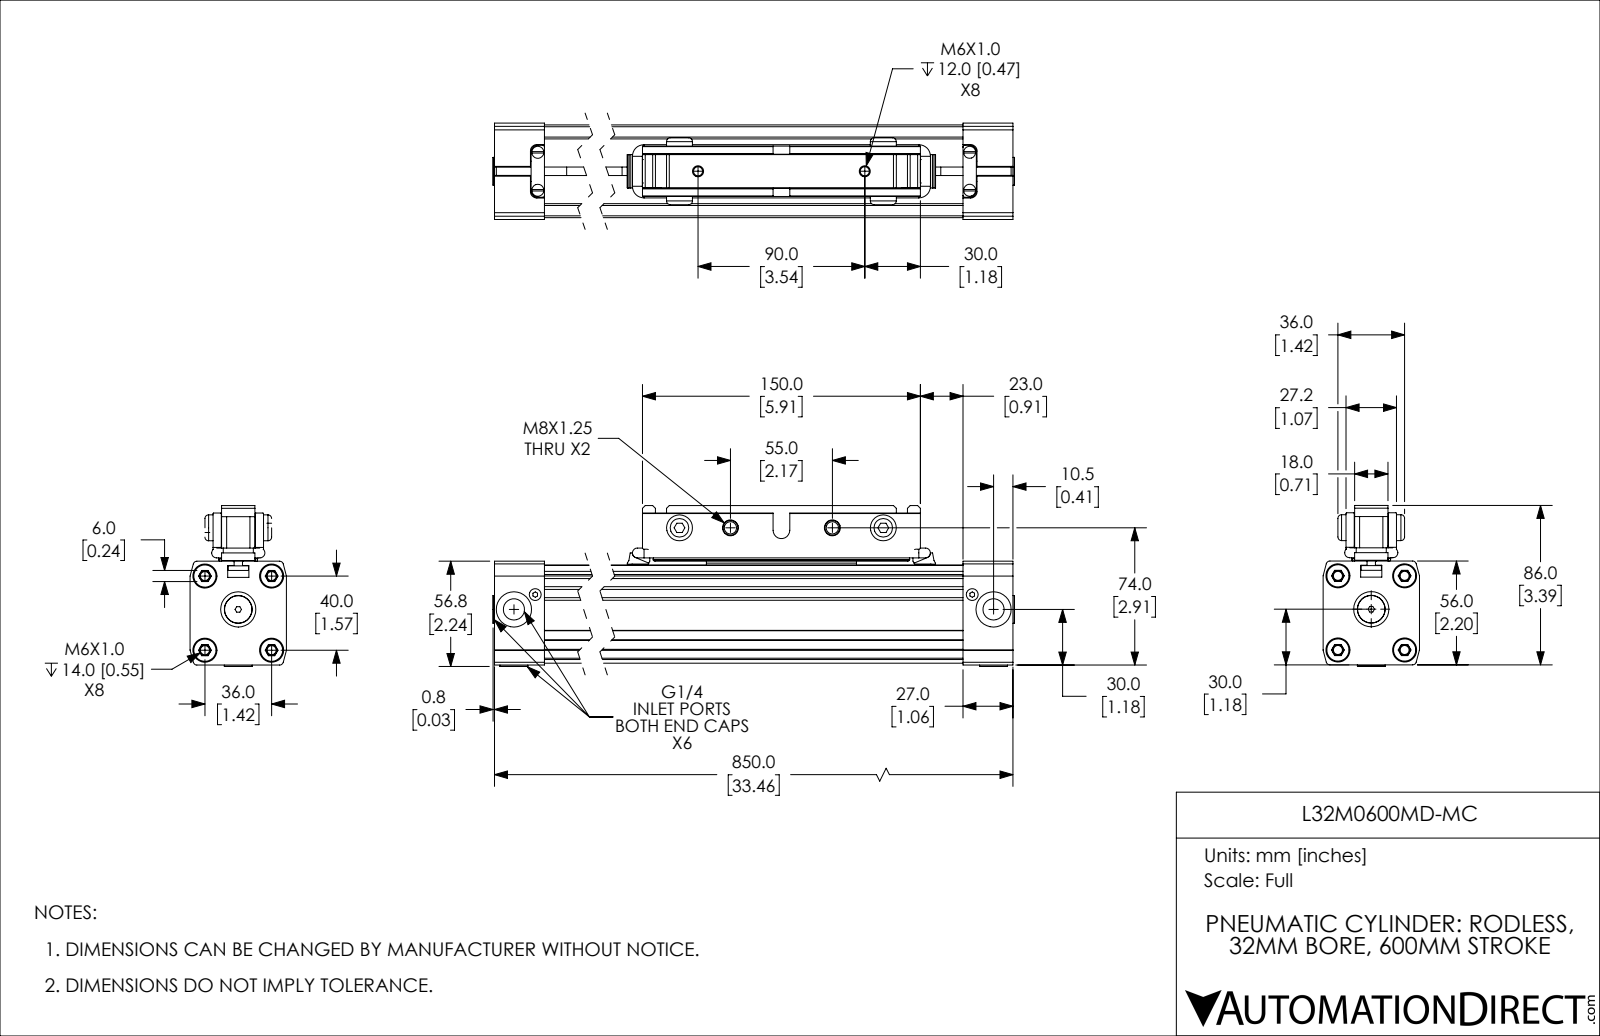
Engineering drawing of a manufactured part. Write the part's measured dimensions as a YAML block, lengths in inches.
part_name: "L32M0600MD-MC_PISTON; L32M0600MD-MC; L32M0600MD-MC_BODY"
step_written_by: "SolidWorks 2019 (CONFIG_CONTROL_DESIGN)"
units: inches
bodies: {solids: 13, faces: 822, planar: 433, cylindrical: 273, other: 116}
overall_size: [33.526, 3.417, 2.047]
volume: 98.32
surface_area: 604.9
round_holes:
  - {diameter: 0.194, count: 6}
  - {diameter: 0.451, count: 5}
  - {diameter: 0.748, count: 5}
  - {diameter: 0.256, count: 4}
  - {diameter: 0.262, count: 4}
  - {diameter: 0.339, count: 4}
  - {diameter: 0.512, count: 4}
  - {diameter: 0.252, count: 2}
  - {diameter: 1.264, count: 1}
round_bosses_or_shafts:
  - {diameter: 0.472, count: 4}
  - {diameter: 0.21, count: 4}
  - {diameter: 0.591, count: 3}
  - {diameter: 0.383, count: 3}
  - {diameter: 0.323, count: 3}
  - {diameter: 0.551, count: 2}
  - {diameter: 1.26, count: 1}
  - {diameter: 1.252, count: 1}
partial_cylinders:
  - {radius: 0.039, count: 22}
  - {radius: 0.079, count: 18}
  - {radius: 0.138, count: 8}
  - {radius: 0.012, count: 4}
  - {radius: 0.02, count: 4}
  - {radius: 0.024, count: 4}
  - {radius: 0.157, count: 4}
  - {radius: 0.006, count: 2}
face_to_face_distances: [2.087, 1.969, 0.201, 0.445, 1.072, 0.181, 0.894, 1.075, 1.768, 0.454]
hole_center_spacings: [0.649, 32.132, 0.552, 0.807, 0.935, 1.002, 1.083, 1.119]
